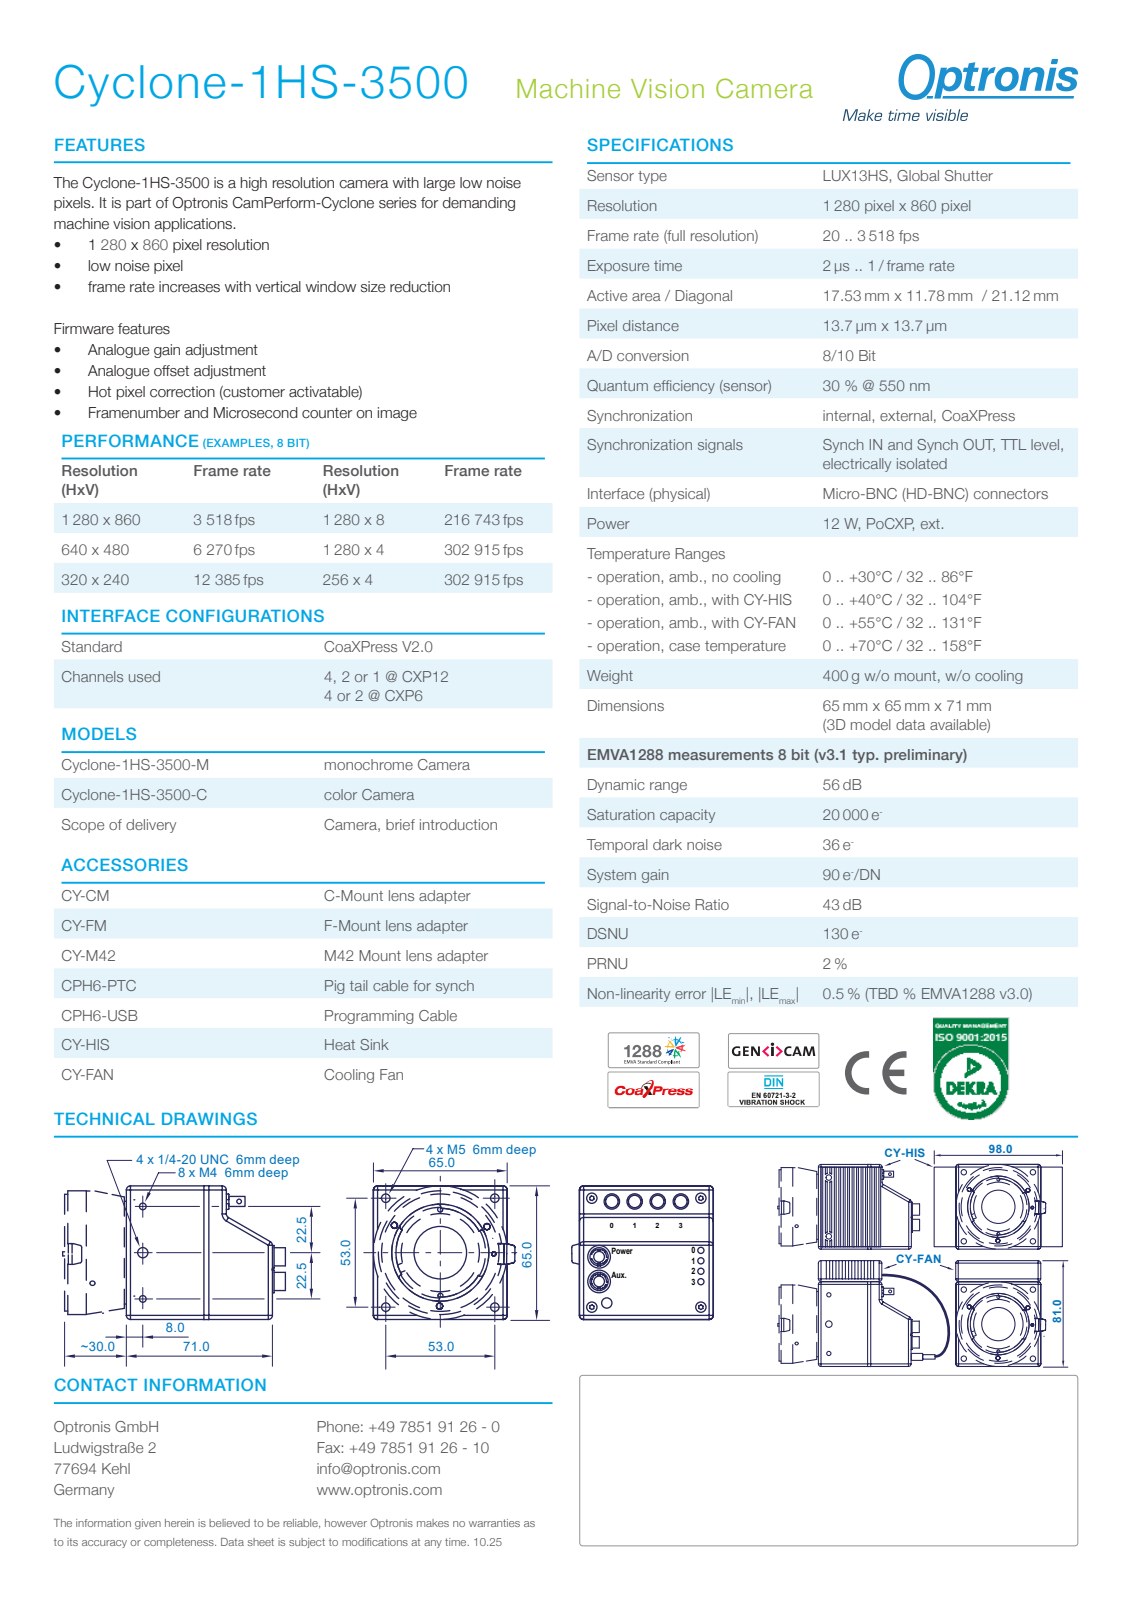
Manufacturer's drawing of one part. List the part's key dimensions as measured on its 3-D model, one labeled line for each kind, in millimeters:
Part name (STEP PRODUCT): 1200-MG-01-D_Cyclone
STEP written by: Autodesk Inventor 2026 (AUTOMOTIVE_DESIGN)
Units: millimetres
Bodies: 7 solids, 3867 faces (1928 planar, 1424 cylindrical, 515 other)
Overall size (bounding box): 77.3 × 65.02 × 65
Volume: 84 869 mm³ · Surface area: 68 675 mm²
Round holes (diameter × count): ⌀0.8 ×18, ⌀0.5 ×10, ⌀1.57 ×8, ⌀0.45 ×4, ⌀0.46 ×4, ⌀2.7 ×4, ⌀2.8 ×4, ⌀3.05 ×4, ⌀3.24 ×4, ⌀3.59 ×4, ⌀3.6 ×4, ⌀4 ×4
Round bosses / shafts (diameter × count): ⌀0.86 ×345, ⌀0.3 ×345, ⌀1.1 ×10, ⌀7.5 ×4, ⌀6.32 ×4, ⌀5.2 ×4, ⌀4.55 ×4, ⌀4.5 ×4
Partial cylindrical surfaces — rounded edges, fillets, slot ends (radius × count): R3 ×36, R1 ×28, R2 ×22, R0.5 ×12, R0.2 ×10, R0.45 ×10, R0.16 ×8, R2.1 ×4
Main face-to-face distances: 2, 63, 65, 61, 59, 3, 58.5, 0.5, 4.8, 28.4
Hole centre spacings: 11.2, 22.5, 1.6, 2.26, 22.4, 53, 5.08, 11.1
